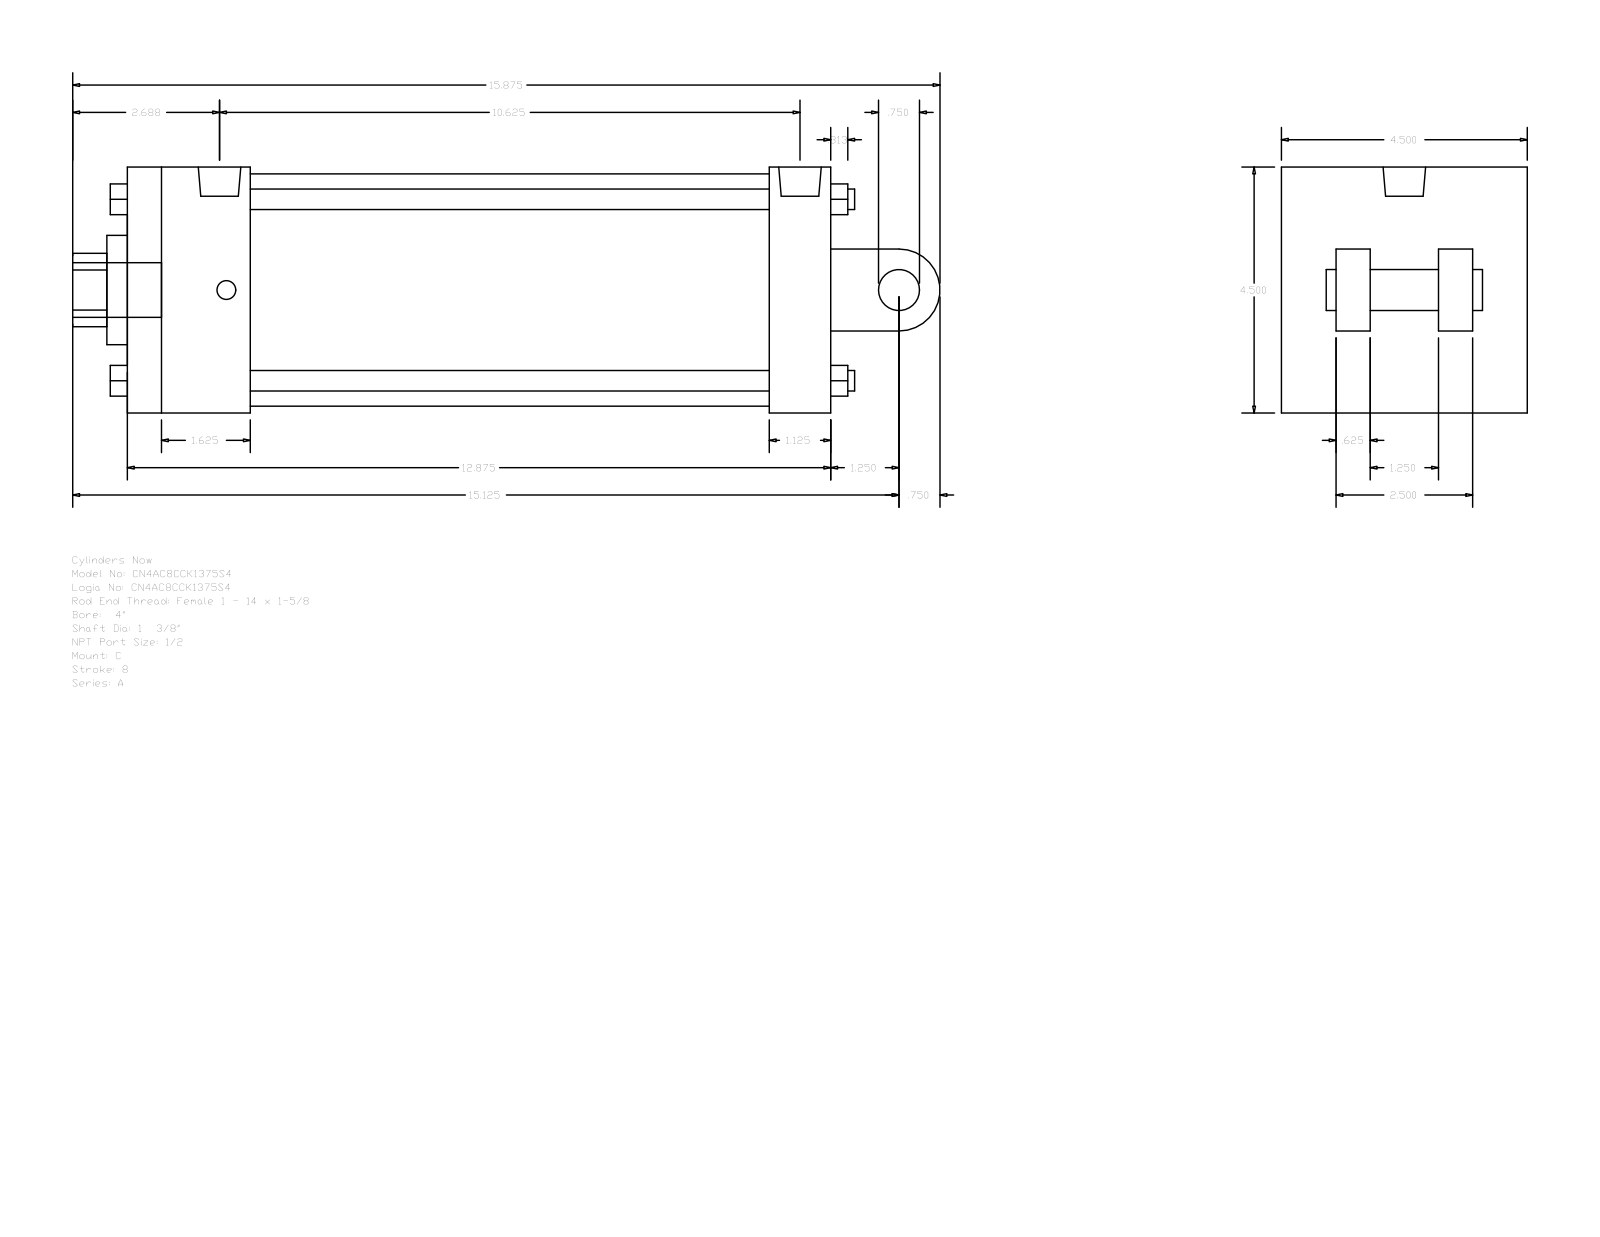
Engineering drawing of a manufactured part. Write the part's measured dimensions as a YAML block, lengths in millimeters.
part_name: "A_C__0400_1.375"
step_written_by: "GSSL Pune (CONFIG_CONTROL_DESIGN)"
units: millimeters
bodies: {solids: 0, faces: 135, planar: 102, cylindrical: 33, other: 0}
overall_size: [403.23, 114.3, 114.3]
round_holes:
  - {diameter: 8.73, count: 2}
  - {diameter: 19.77, count: 1}
  - {diameter: 34.92, count: 1}
  - {diameter: 50.8, count: 1}
  - {diameter: 107.95, count: 1}
round_bosses_or_shafts:
  - {diameter: 9.53, count: 4}
  - {diameter: 8.73, count: 2}
  - {diameter: 25.4, count: 1}
  - {diameter: 19.77, count: 1}
  - {diameter: 19.05, count: 1}
partial_cylinders:
  - {radius: 17.06, count: 1}
  - {radius: 19.05, count: 1}
face_to_face_distances: [114.3, 327.03, 28.58, 73.03, 298.45, 57.15, 241.3, 269.88, 15.87, 41.27]
hole_center_spacings: [3.18]
